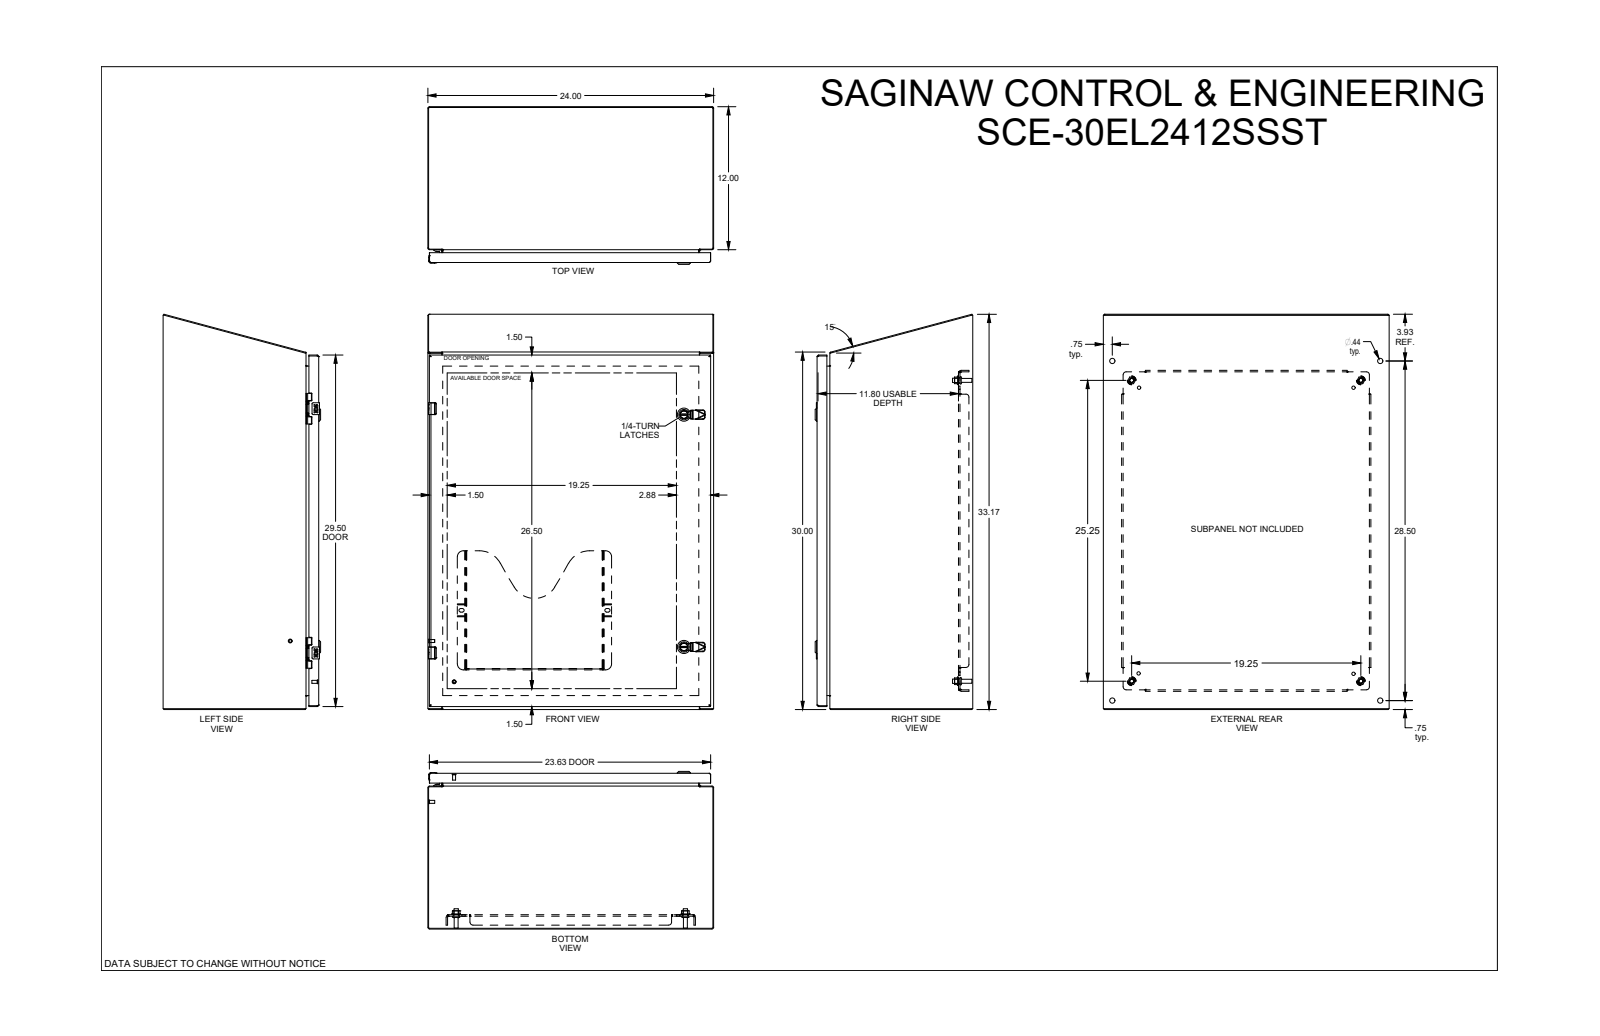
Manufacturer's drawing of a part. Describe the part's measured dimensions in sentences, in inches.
The part is named "SCE-30EL2412SSST". Its 3-D file was written by "SolidWorks 2019 (CONFIG_CONTROL_DESIGN)". It is 0 solids with 2844 faces: 1311 planar, 759 cylindrical and 774 other. Overall it measures 33.178 by 24 by 13.23 inches. Round holes: 4 of diameter 0.172, 4 of diameter 0.205, 4 of diameter 0.244, 4 of diameter 0.266, 4 of diameter 0.281, 4 of diameter 0.367, 4 of diameter 0.375, 4 of diameter 0.437, 4 of diameter 0.5, 2 of diameter 0.156, 2 of diameter 0.197, 2 of diameter 0.218. Round bosses or shafts: 6 of diameter 0.17, 4 of diameter 0.366, 4 of diameter 0.332, 4 of diameter 0.25, 4 of diameter 0.248, 3 of diameter 0.196, 2 of diameter 1.102, 2 of diameter 0.866. Partial cylindrical surfaces (rounded edges, fillets, slot ends): 56 of radius 0.012, 32 of radius 0.015, 28 of radius 0.01, 23 of radius 0.04, 20 of radius 0.02, 12 of radius 0.029, 11 of radius 0.06, 10 of radius 0.07. The main face-to-face distances are 0.075, 0.075, 12.998, 12.923, 23.925, 13.073, 12.998, 1.2, 11.873, 1. The hole center spacings are 20.5, 0.985, 0.02, 0.875, 4.493, 20.938, 3.173, 18.641.
